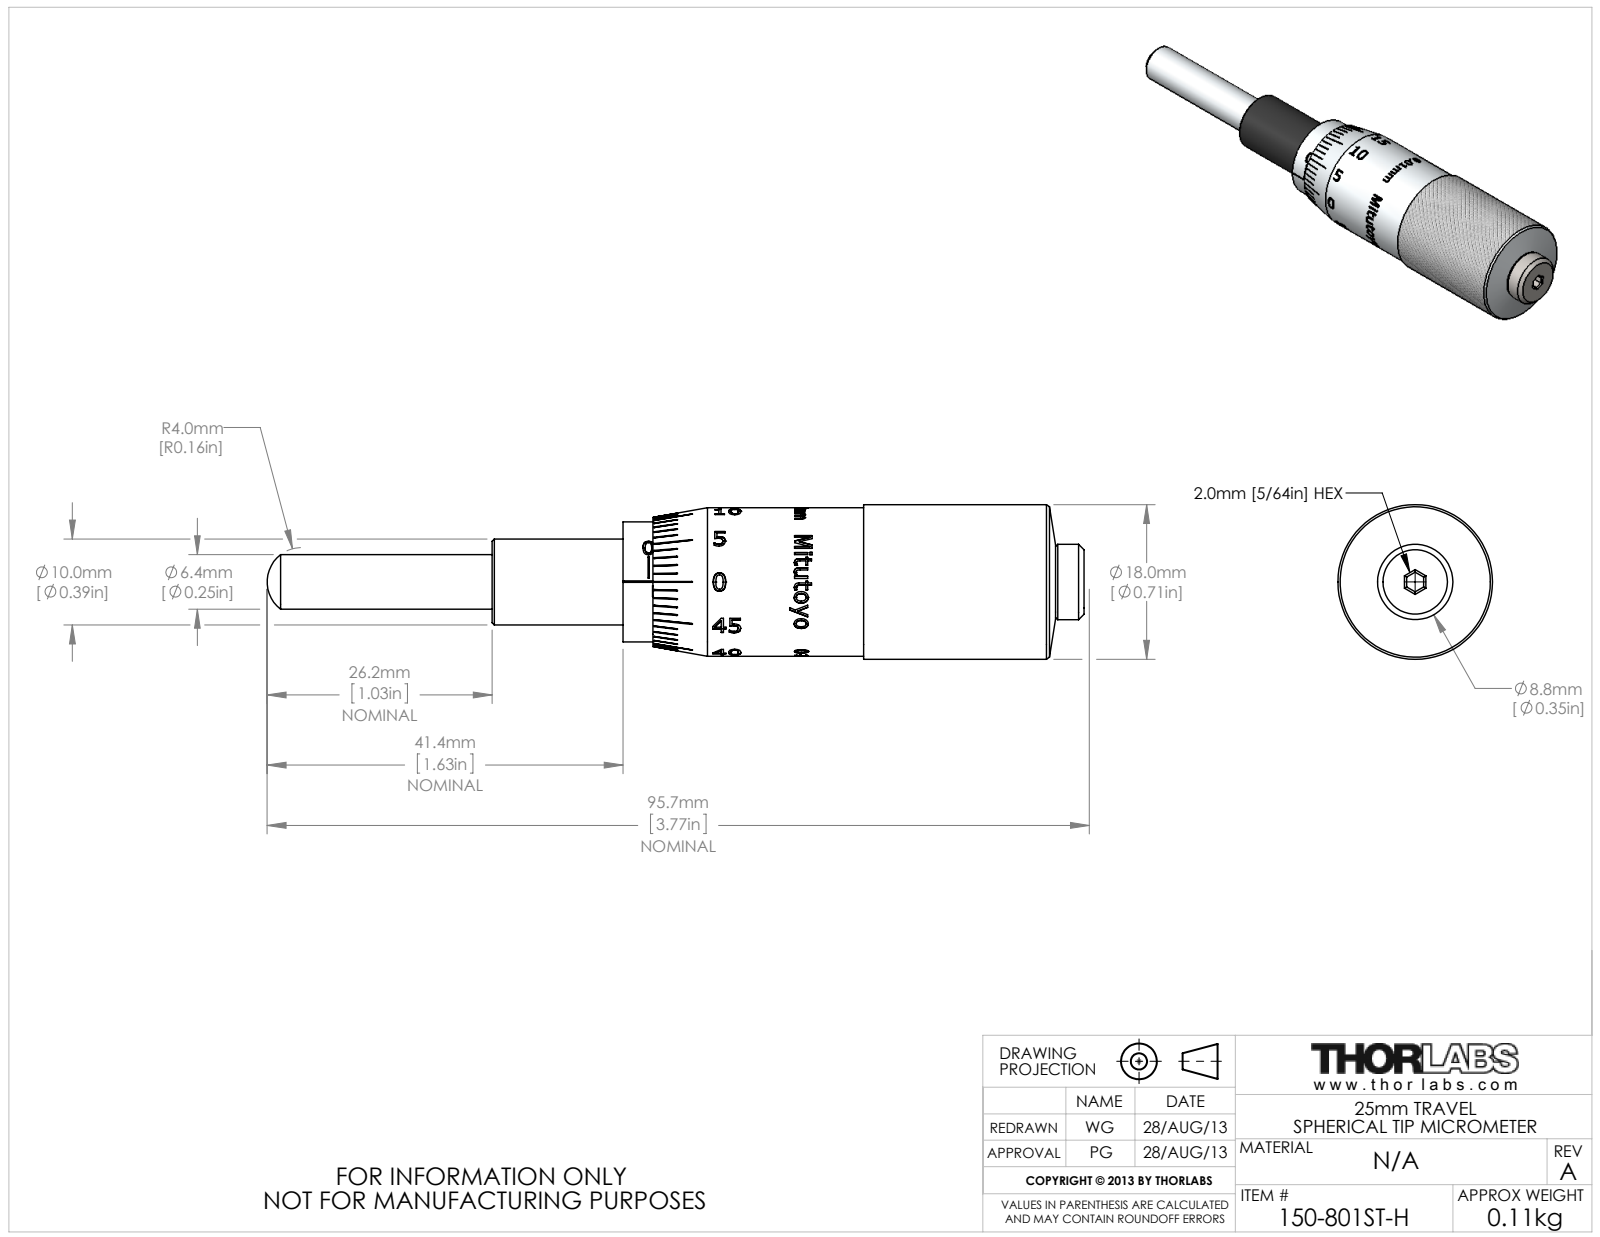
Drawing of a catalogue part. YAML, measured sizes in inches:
part_name: "TTN016868; TTN017212-E0W; TTN016889"
step_written_by: "SolidWorks 2012 (AUTOMOTIVE_DESIGN)"
units: inches
bodies: {solids: 2, faces: 944, planar: 366, cylindrical: 175, other: 403}
overall_size: [3.744, 0.709, 0.709]
volume: 0.847
surface_area: 7.005
round_holes:
  - {diameter: 0.157, count: 1}
round_bosses_or_shafts:
  - {diameter: 0.709, count: 1}
  - {diameter: 0.68, count: 1}
  - {diameter: 0.55, count: 1}
  - {diameter: 0.394, count: 1}
  - {diameter: 0.345, count: 1}
  - {diameter: 0.25, count: 1}
  - {diameter: 0.137, count: 1}
partial_cylinders:
  - {radius: 0.267, count: 1}
  - {radius: 0.274, count: 1}
  - {radius: 0.276, count: 1}
  - {radius: 0.297, count: 1}
  - {radius: 0.315, count: 1}
  - {radius: 0.327, count: 1}
  - {radius: 0.339, count: 1}
face_to_face_distances: [1.982, 0.6, 2.582, 2.713, 2.113, 0.13, 0.737, 0.137, 1.845, 1.976]
